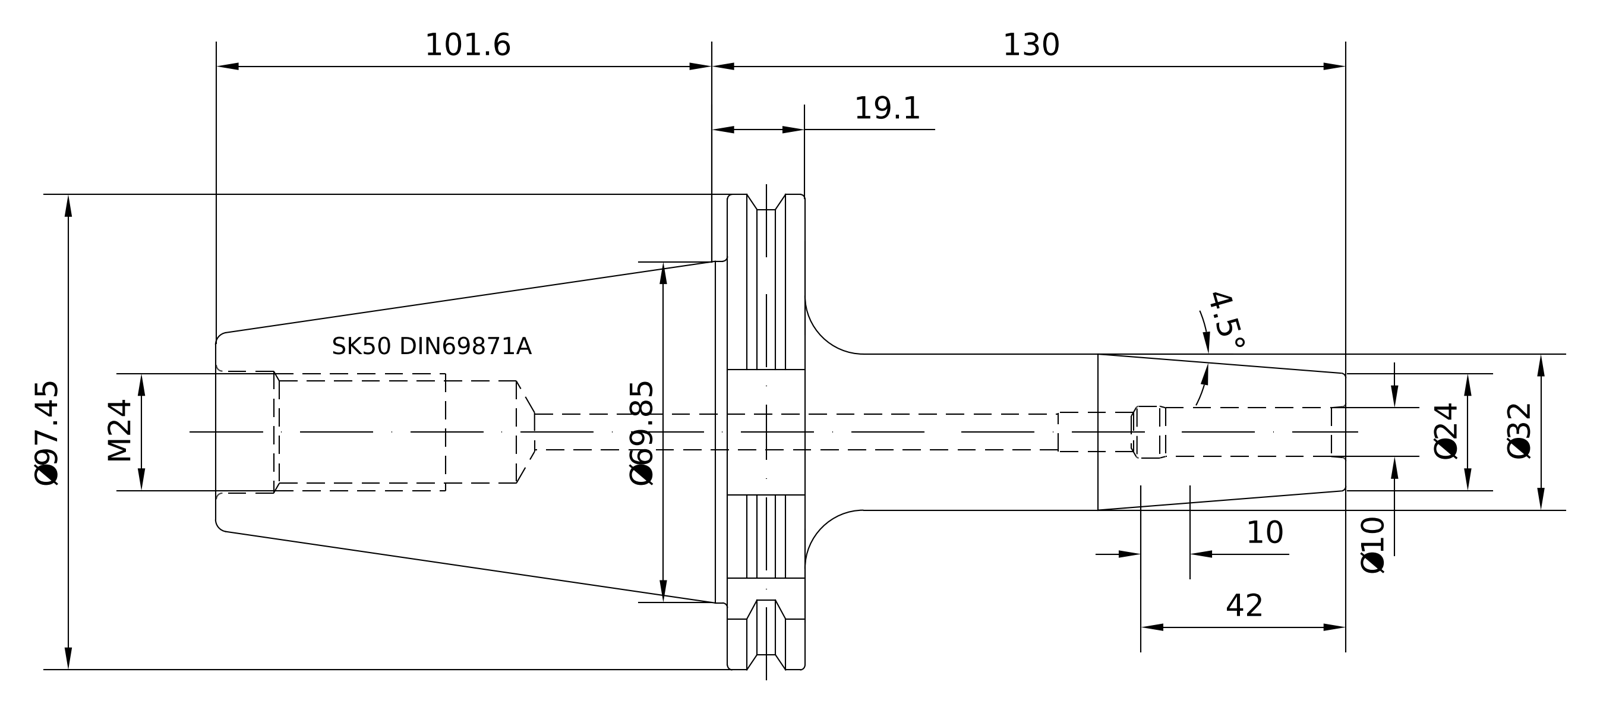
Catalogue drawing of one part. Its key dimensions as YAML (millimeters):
part_name: "50-444-10"
step_written_by: "PRO/ENGINEER BY PARAMETRIC TECHNOLOGY CORPORATION, 2010430 (CONFIG_CONTROL_DESIGN)"
units: millimeters
bodies: {solids: 1, faces: 93, planar: 21, cylindrical: 24, other: 48}
overall_size: [231.6, 97.47, 94]
volume: 419514
surface_area: 53658
round_holes:
  - {diameter: 10, count: 1}
  - {diameter: 20.75, count: 1}
  - {diameter: 25.01, count: 1}
  - {diameter: 25.7, count: 1}
round_bosses_or_shafts:
  - {diameter: 91, count: 1}
  - {diameter: 69.15, count: 1}
  - {diameter: 32, count: 1}
  - {diameter: 24.01, count: 1}
partial_cylinders:
  - {radius: 1.75, count: 1}
  - {radius: 48.74, count: 1}
face_to_face_distances: [15.85, 72.8, 104.8, 120.65, 231.6, 126.8, 110.95, 25.8, 48, 56.8]
